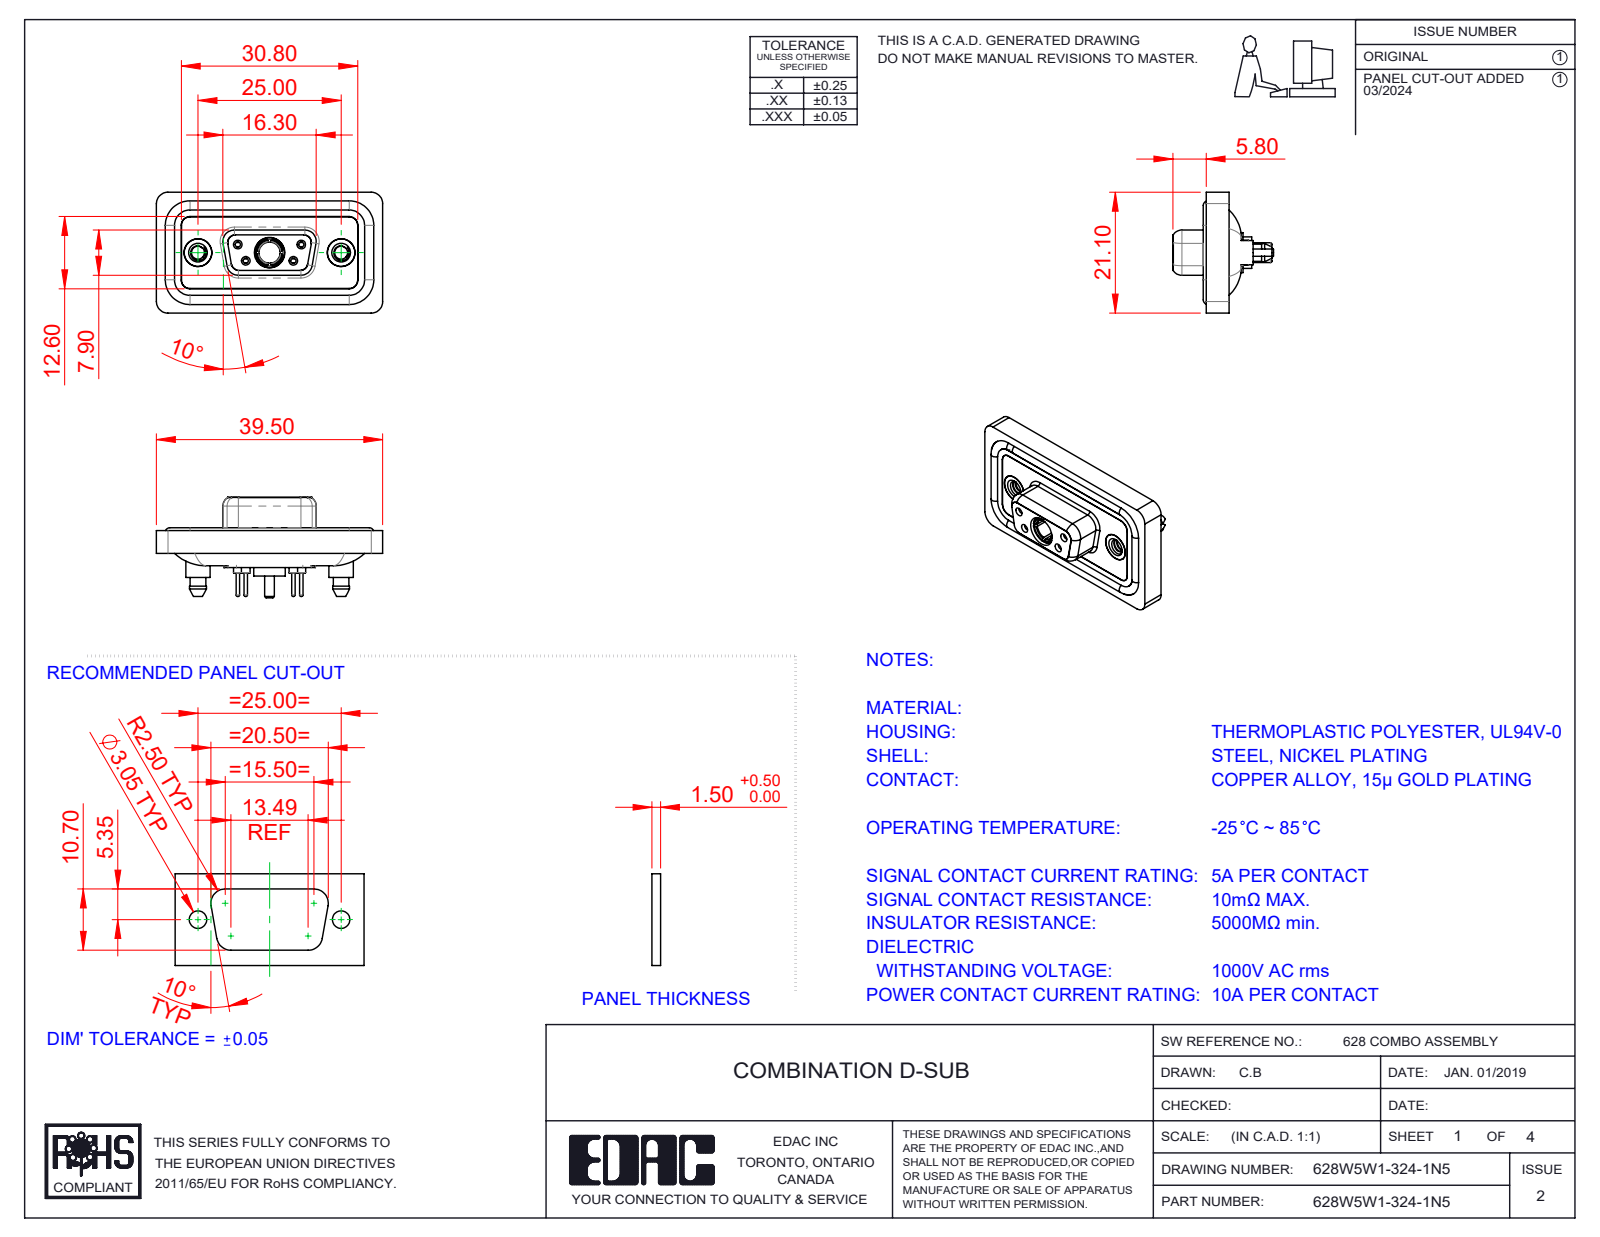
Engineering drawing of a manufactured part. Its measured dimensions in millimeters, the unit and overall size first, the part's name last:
Units: millimetres
Overall size (bounding box): 39.5 × 21.1 × 17.55
Round holes (diameter × count): ⌀0.9 ×4, ⌀1.1 ×4, ⌀1.5 ×4, ⌀2 ×4, ⌀4.85 ×3, ⌀1.6 ×2, ⌀1.7 ×2, ⌀2.26 ×2, ⌀4 ×2, ⌀4.05 ×2, ⌀5 ×2, ⌀3.7 ×1
Round bosses / shafts (diameter × count): ⌀1.6 ×6, ⌀2.2 ×4, ⌀0.6 ×4, ⌀5.4 ×2, ⌀4.95 ×2, ⌀4.8 ×2, ⌀4.25 ×2, ⌀5.5 ×1
Partial cylindrical surfaces — rounded edges, fillets, slot ends (radius × count): R1.5 ×24, R2 ×18, R1.6 ×10, R1.35 ×8, R0.25 ×4, R0.5 ×4, R0.6 ×4, R0.65 ×4
Main face-to-face distances: 0.4, 2.9, 1.8, 1.1, 1.6, 0.5, 5.65, 7.45, 5.35, 3.6
Hole centre spacings: 3.16, 5.72, 7.1, 12.5, 18.1, 4.39, 4.4, 8.31
Volume: 4 886 mm³ · Surface area: 7 956 mm²
Bodies: 13 solids, 730 faces (210 planar, 319 cylindrical, 201 other)
Part name (STEP PRODUCT): 628Combo Shell Front_09 Contacts; 628Combo Contact Row 2_24; 628Combo Shell Rear_09 Contacts; 628Combo Housing_5W1 (+5 more)
STEP written by: SolidWorks 2023 (CONFIG_CONTROL_DESIGN)
